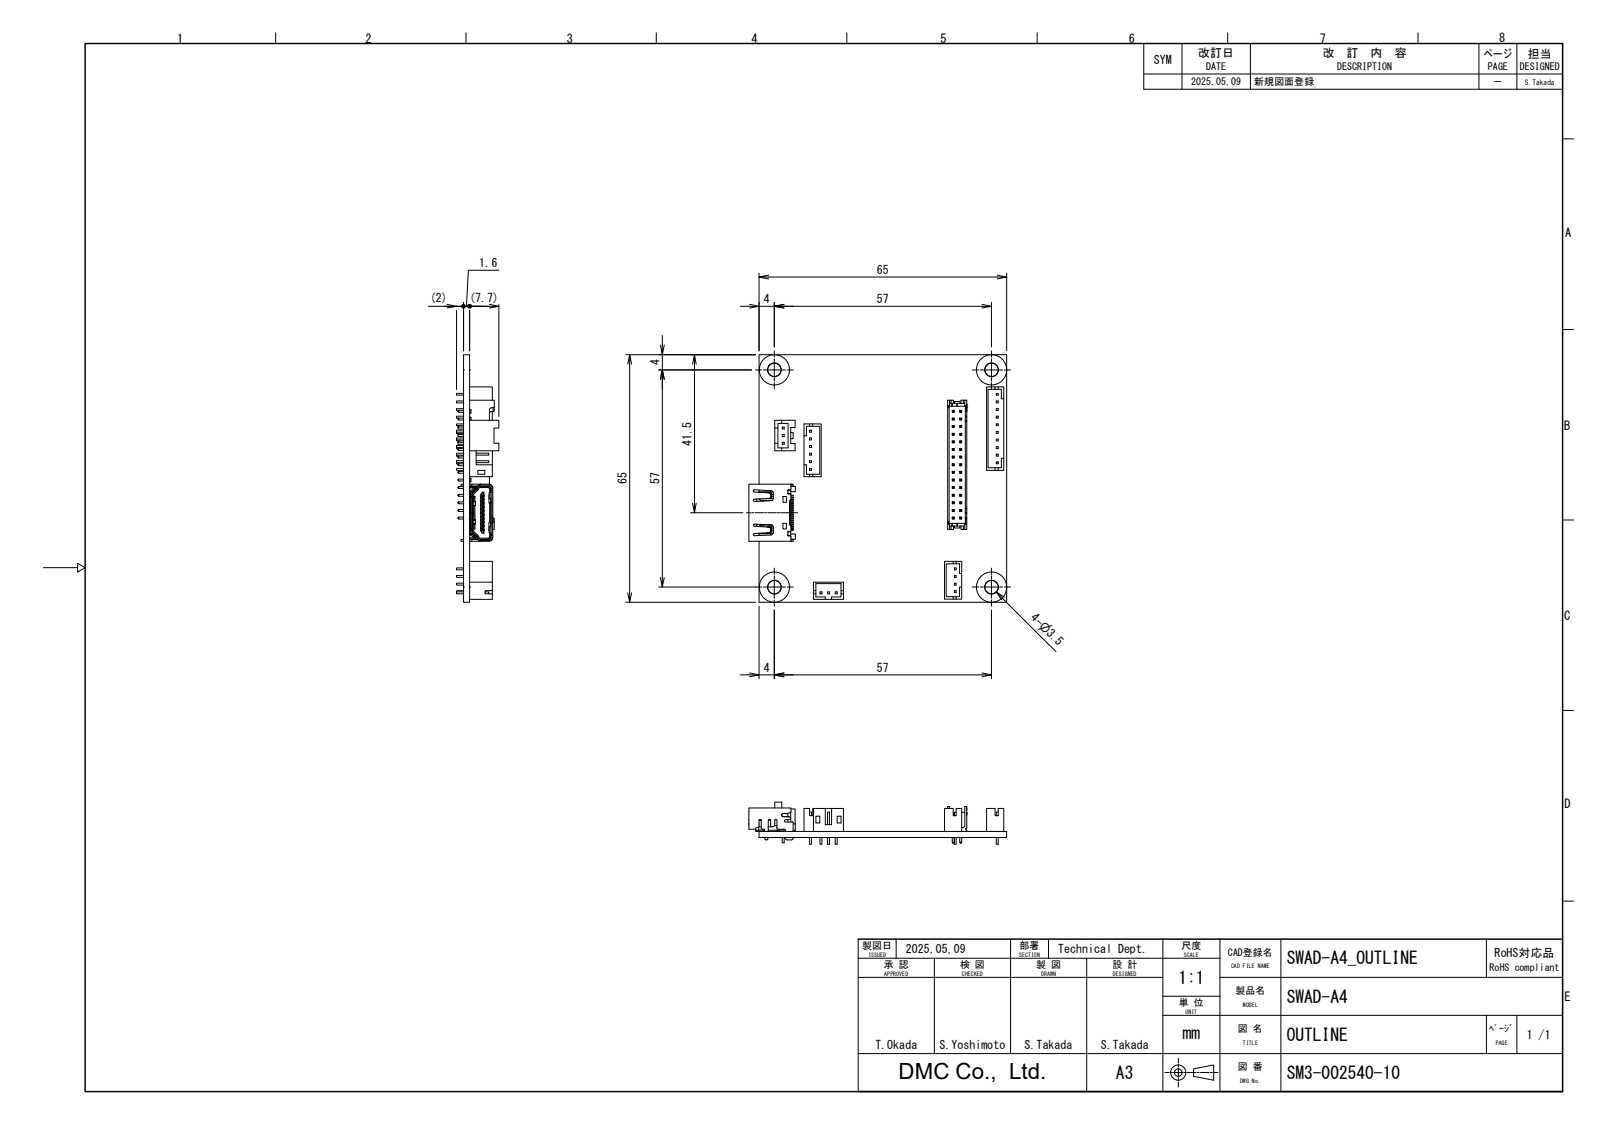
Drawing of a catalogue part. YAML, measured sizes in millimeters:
step_written_by: "Autodesk Inventor 2024 (AUTOMOTIVE_DESIGN)"
units: millimeters
bodies: {solids: 1, faces: 2838, planar: 2466, cylindrical: 287, other: 85}
overall_size: [67.7, 65, 11.1]
volume: 8350
surface_area: 13108
round_holes:
  - {diameter: 3.5, count: 4}
  - {diameter: 8, count: 4}
round_bosses_or_shafts:
  - {diameter: 3.6, count: 4}
partial_cylinders:
  - {radius: 0.1, count: 39}
  - {radius: 0.3, count: 22}
  - {radius: 0.5, count: 21}
  - {radius: 0.15, count: 20}
  - {radius: 0.2, count: 17}
  - {radius: 1, count: 12}
  - {radius: 0.25, count: 9}
  - {radius: 0.35, count: 5}
face_to_face_distances: [1.6, 1.59, 4.5, 4.1, 0.5, 0.4, 3.35, 0.35, 4.65, 0.8]
hole_center_spacings: [57, 80.61]
